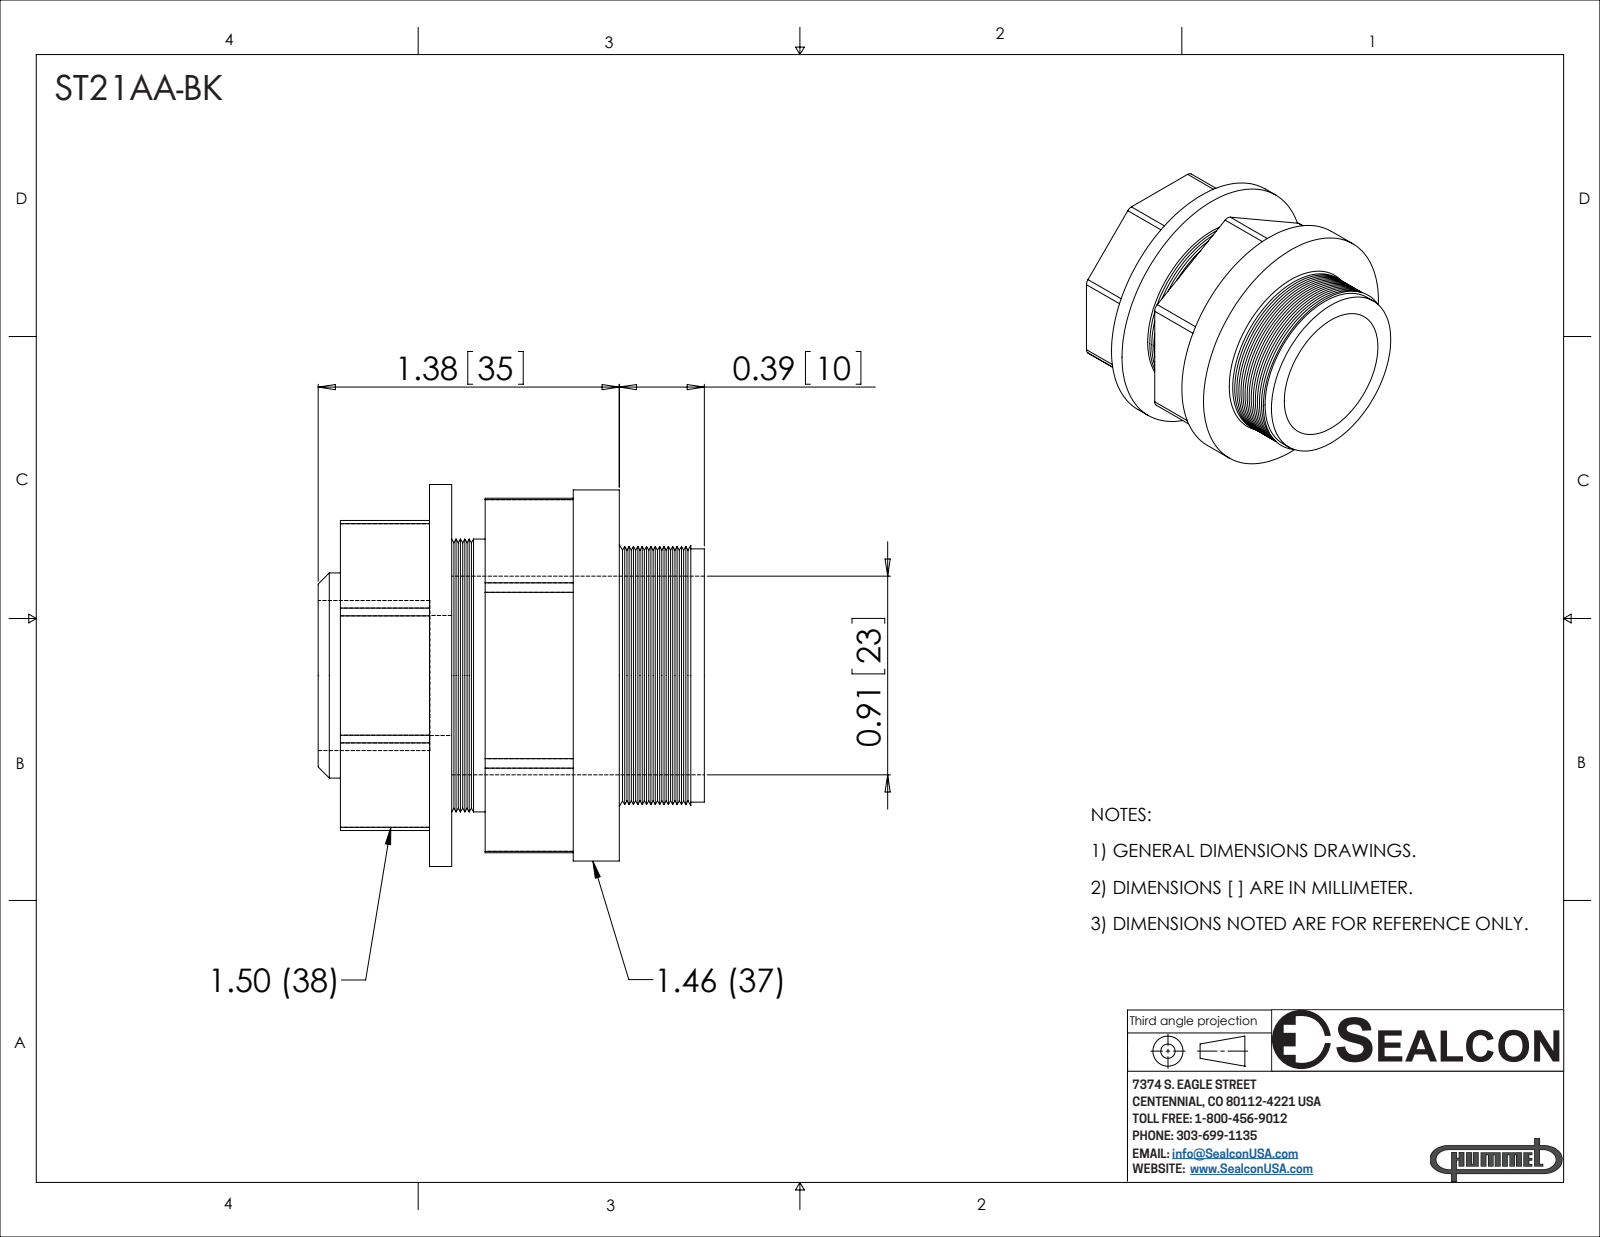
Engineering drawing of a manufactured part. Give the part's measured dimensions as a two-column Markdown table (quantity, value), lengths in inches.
| quantity | value |
| --- | --- |
| part name | ST21AA-BK |
| STEP written by | SolidWorks 2008 (CONFIG_CONTROL_DESIGN) |
| units | inches |
| bodies | 2 solids, 141 faces (25 planar, 30 cylindrical, 86 other) |
| overall size | 1.77 × 1.75 × 1.75 |
| volume | 1.811 in³ |
| surface area | 21.55 in² |
| round holes (diameter × count) | 0.55 × 1, 0.687 × 1, 0.91 × 1 |
| round bosses / shafts (diameter × count) | 1.75 × 1, 1.7 × 1, 1.25 × 1, 1.16 × 1, 0.94 × 1 |
| partial cylindrical surfaces (radius × count) | 0.05 × 14 |
| main face-to-face distances | 1.42, 0.51, 0.768, 1.278, 0.102, 0.408, 0.87, 1.067, 0.659, 0.557 |
